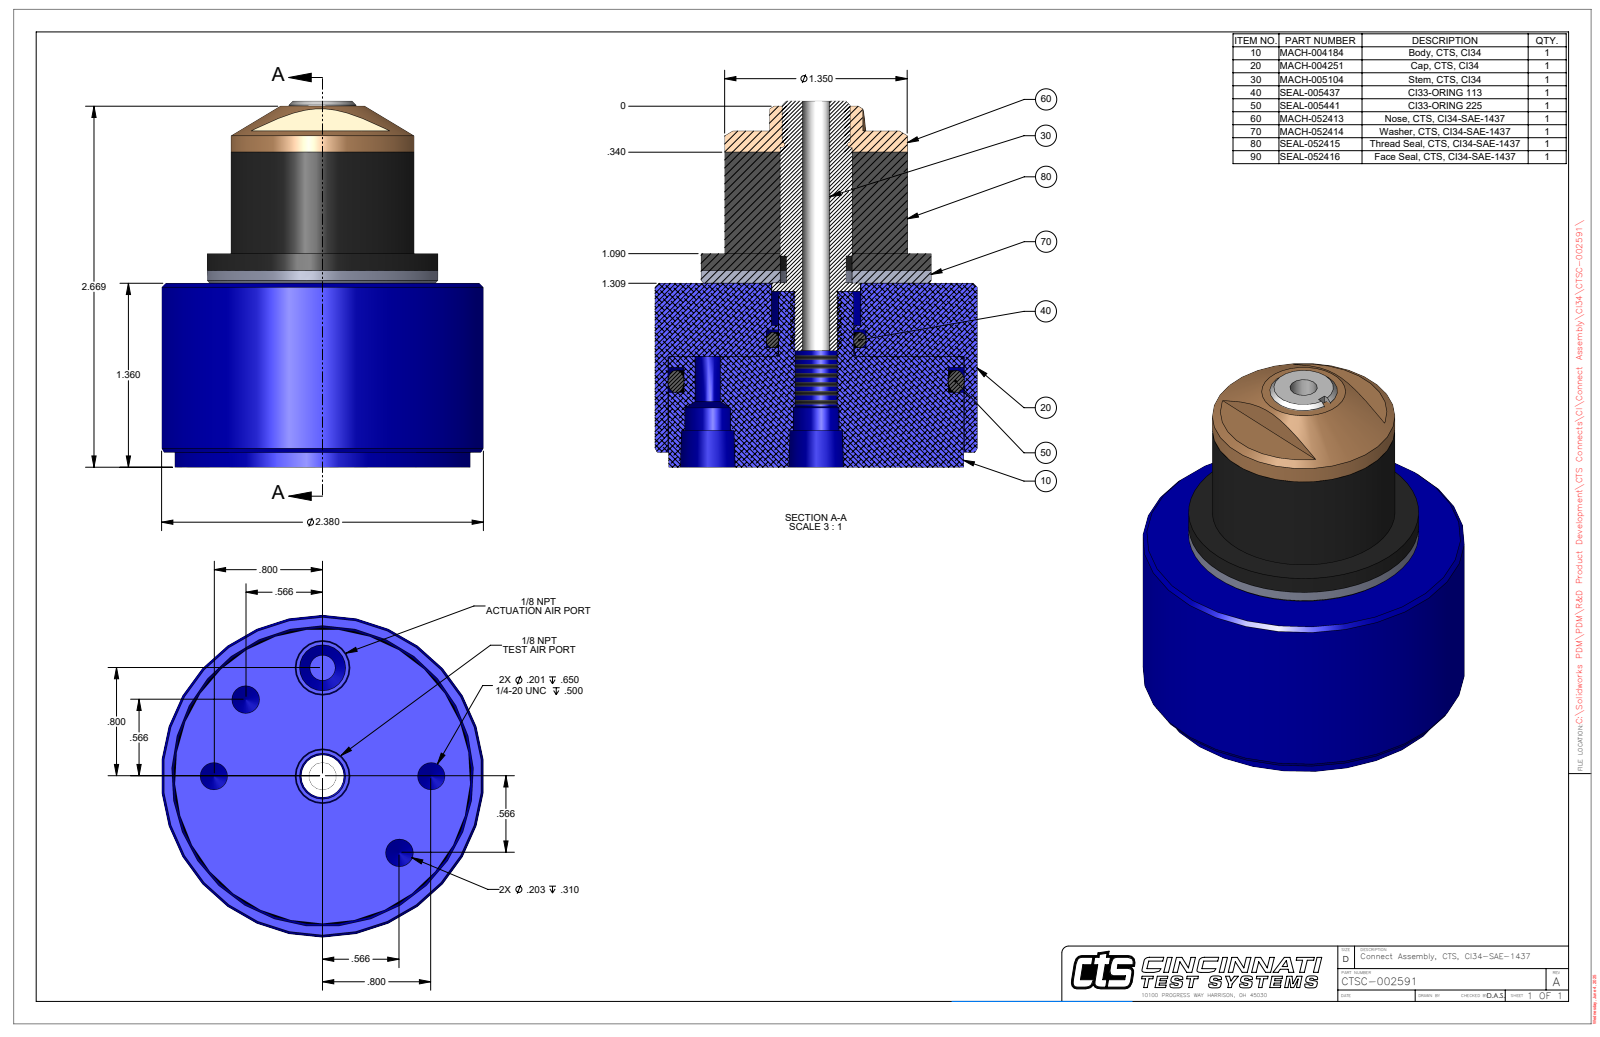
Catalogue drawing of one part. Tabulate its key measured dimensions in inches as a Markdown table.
| quantity | value |
| --- | --- |
| part name | CTSC-002591 |
| STEP written by | SolidWorks 2023 (AUTOMOTIVE_DESIGN) |
| units | inches |
| bodies | 1 solid, 80 faces (23 planar, 32 cylindrical, 25 other) |
| overall size | 2.706 × 2.38 × 2.38 |
| volume | 7.629 in³ |
| surface area | 32.16 in² |
| round holes (diameter × count) | 0.201 × 2, 0.203 × 2, 0.339 × 2, 0.203 × 1, 0.661 × 1, 2.188 × 1 |
| round bosses / shafts (diameter × count) | 2.38 × 1, 2.178 × 1, 1.7 × 1, 1.35 × 1, 0.65 × 1, 0.5 × 1 |
| partial cylindrical surfaces (radius × count) | 0.211 × 1 |
| main face-to-face distances | 1.36, 1.579, 0.219, 0.11, 1.25, 1.469, 2.485, 2.375, 1.125, 0.906 |
| hole center spacings | 0.8, 0.612, 1.478, 1.131, 1.6 |
